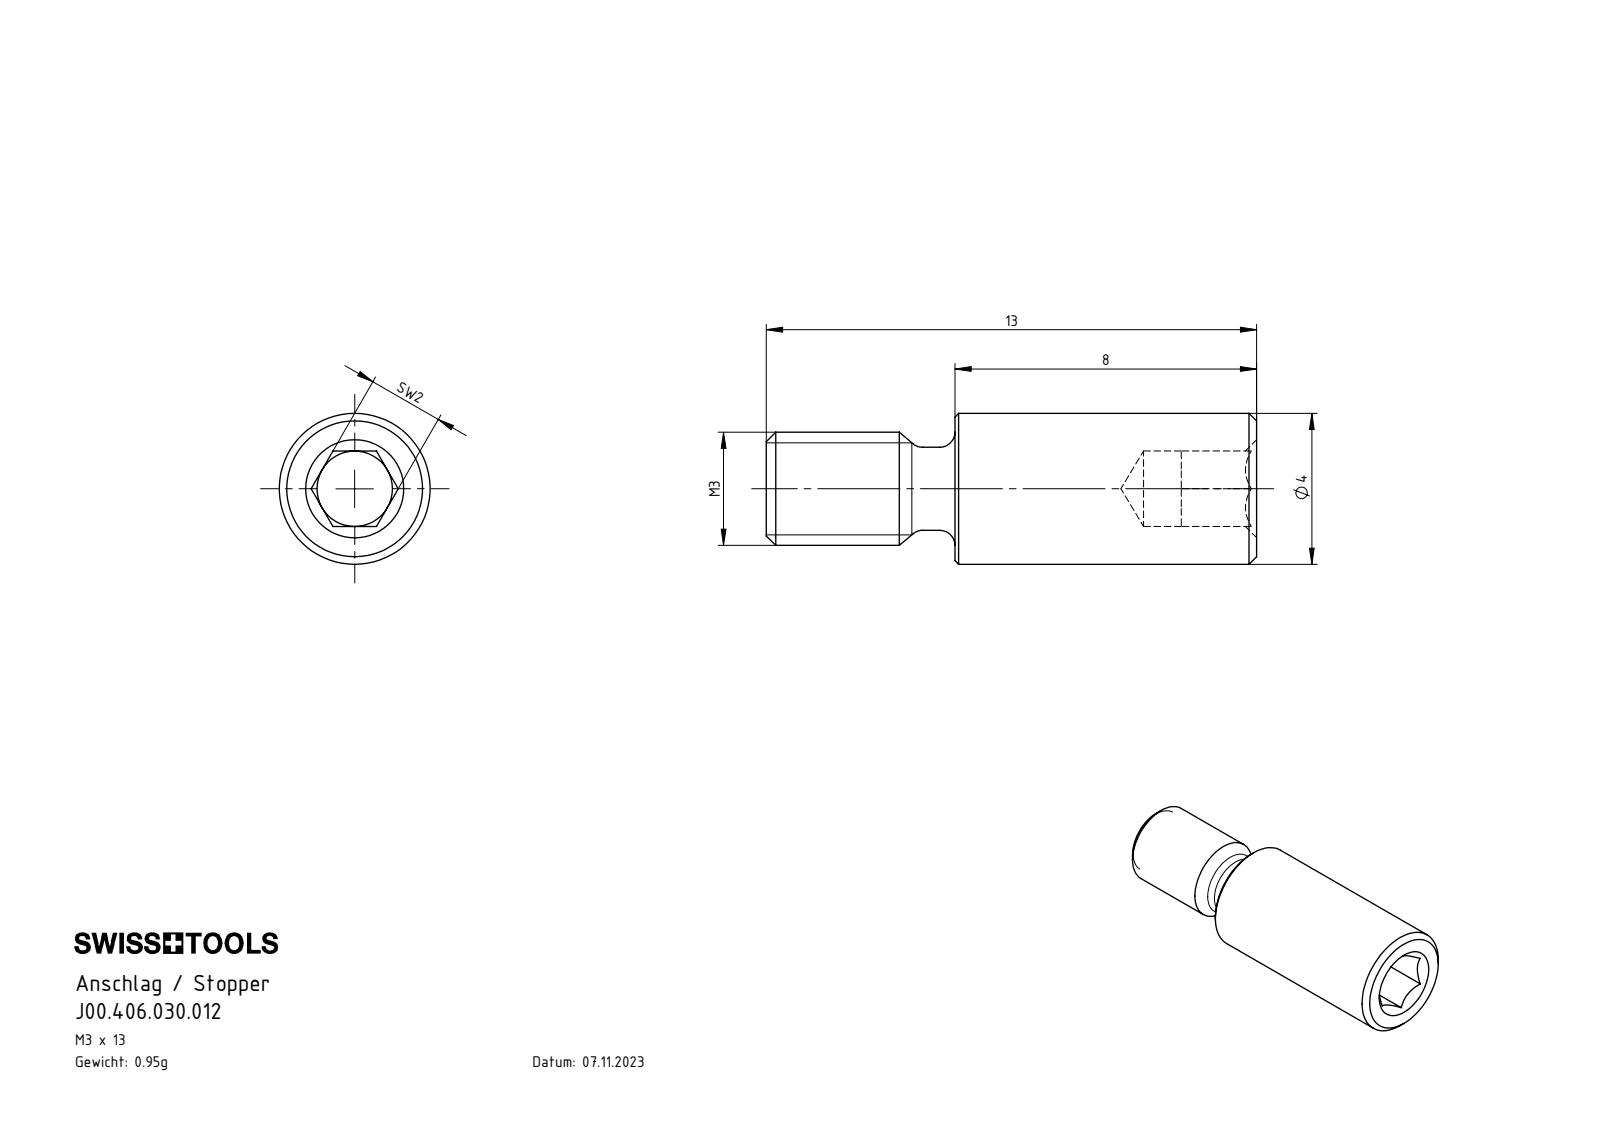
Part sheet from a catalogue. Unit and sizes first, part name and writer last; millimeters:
Units: millimetres
Overall size (bounding box): 13 × 4 × 4
Round holes (diameter × count): ⌀2 ×1
Round bosses / shafts (diameter × count): ⌀4 ×1, ⌀3 ×1, ⌀2.2 ×1
Main face-to-face distances: 2, 13, 5, 8, 11, 6
Volume: 121 mm³ · Surface area: 189 mm²
Bodies: 1 solid, 39 faces (15 planar, 8 cylindrical, 16 other)
Part name (STEP PRODUCT): J00.406.030.012
STEP written by: SolidWorks 2022 (AUTOMOTIVE_DESIGN)
